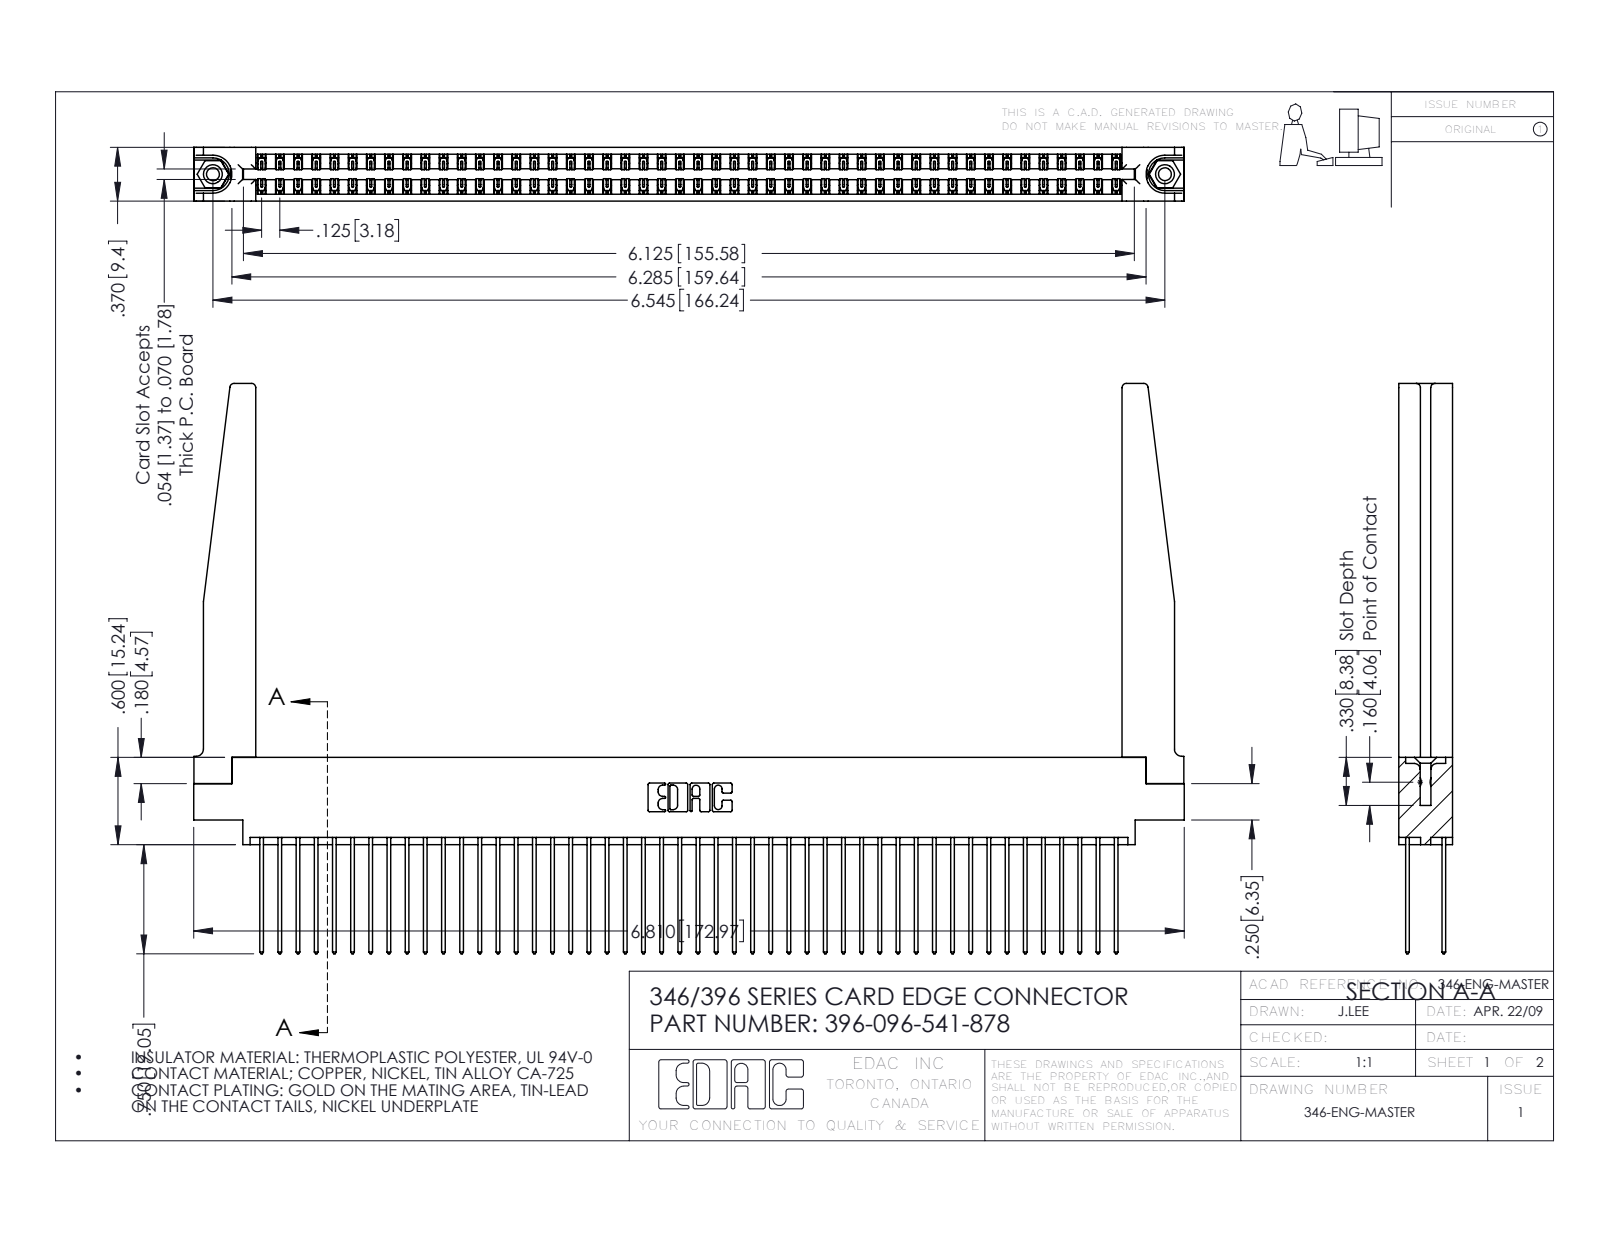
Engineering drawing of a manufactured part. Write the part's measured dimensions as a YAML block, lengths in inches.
part_name: "396-096-541-878; 345-250-001_345-250-001-102; 346-220-078_345-220-078; 346 Part_0.170 Offset - 0.156 Dia-TH (+1 more)"
step_written_by: "SolidWorks 2016 (CONFIG_CONTROL_DESIGN)"
units: inches
bodies: {solids: 101, faces: 5352, planar: 3582, cylindrical: 1718, other: 52}
overall_size: [6.81, 3.92, 0.37]
volume: 1.478
surface_area: 51.53
round_holes:
  - {diameter: 0.089, count: 2}
  - {diameter: 0.125, count: 2}
  - {diameter: 0.156, count: 2}
  - {diameter: 0.064, count: 1}
round_bosses_or_shafts:
  - {diameter: 0.155, count: 2}
partial_cylinders:
  - {radius: 0.006, count: 144}
  - {radius: 0.01, count: 96}
  - {radius: 0.01, count: 22}
  - {radius: 0.03, count: 8}
  - {radius: 0.007, count: 6}
  - {radius: 0.031, count: 6}
  - {radius: 0.026, count: 3}
  - {radius: 0.014, count: 2}
face_to_face_distances: [0.048, 0.322, 0.37, 0.072, 0.25, 0.298, 0.025, 0.275, 0.148, 0.15]
hole_center_spacings: [0.246, 6.336, 6.545]
